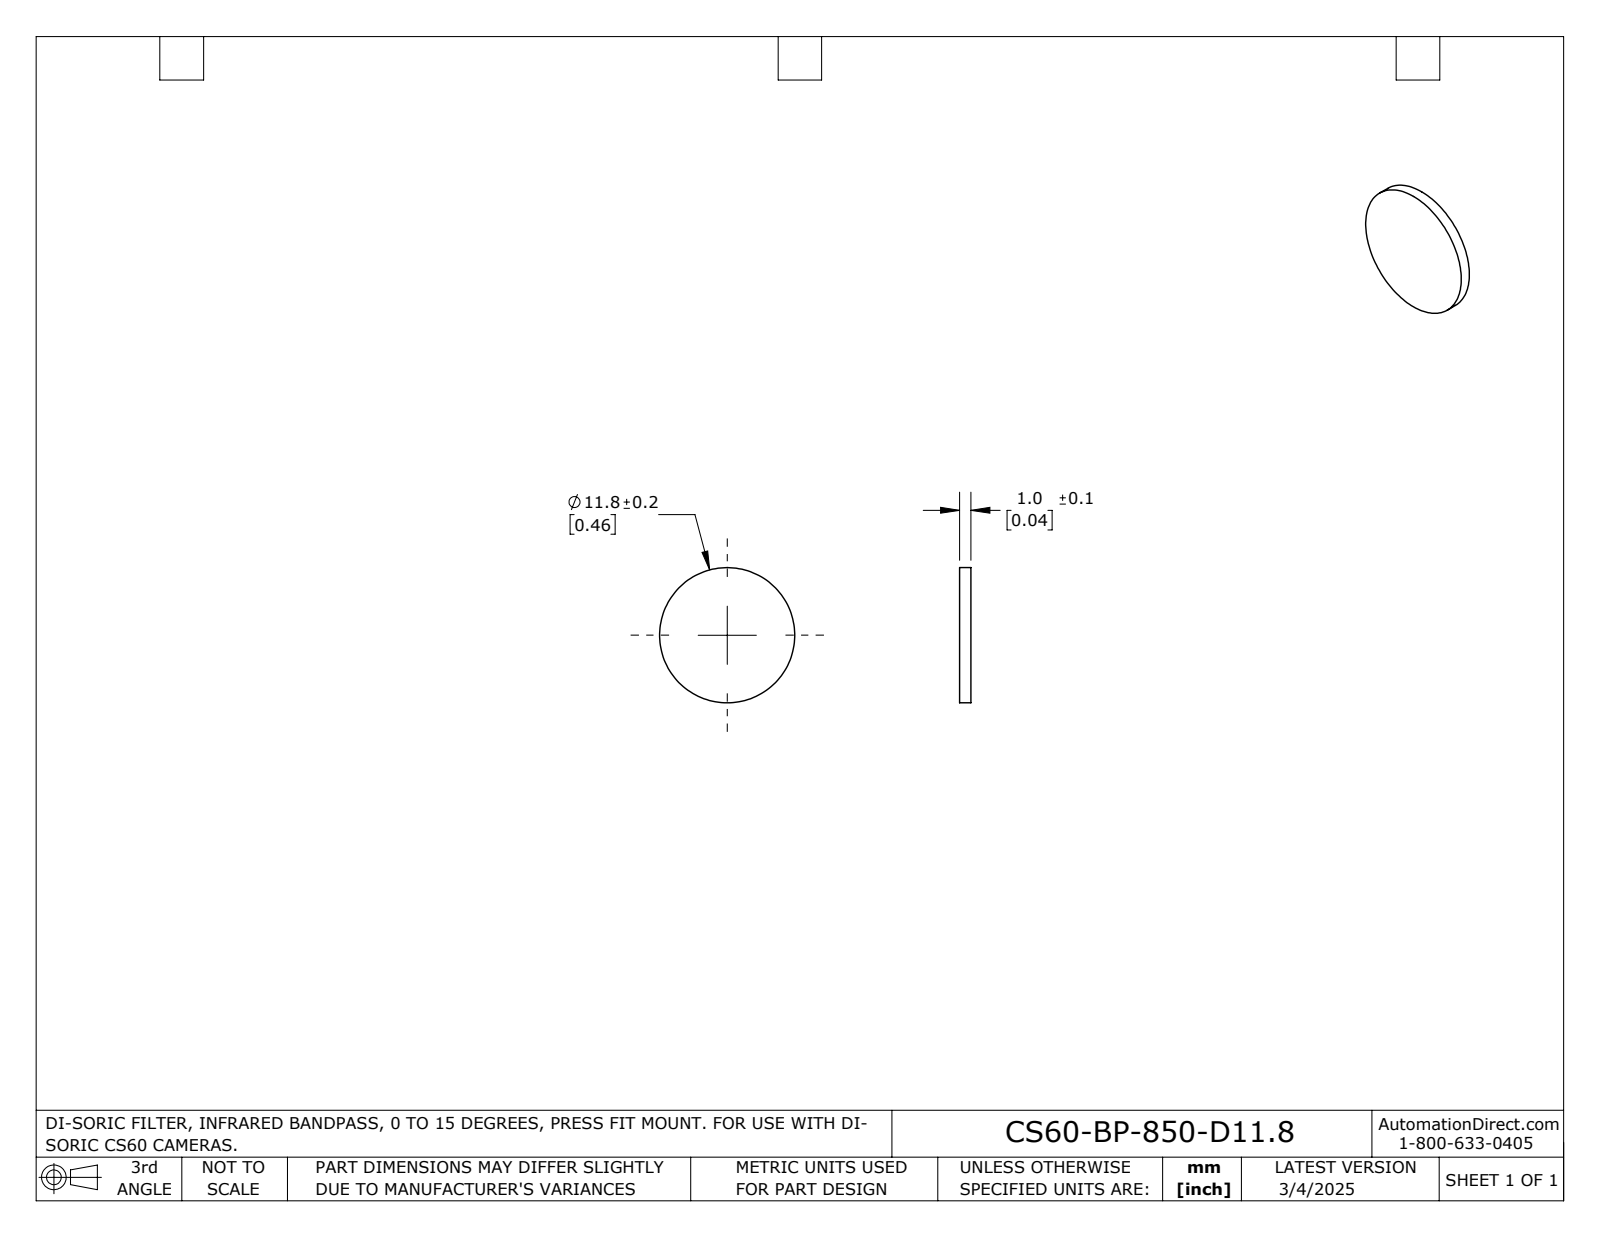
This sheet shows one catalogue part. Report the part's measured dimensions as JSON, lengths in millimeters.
{"part_name": "CS60-BP-xxx-D11.8", "step_written_by": "SolidWorks 2024 (AUTOMOTIVE_DESIGN)", "units": "millimeters", "bodies": {"solids": 1, "faces": 3, "planar": 2, "cylindrical": 1, "other": 0}, "overall_size": [11.8, 11.8, 1], "volume_mm3": 109, "surface_area_mm2": 256, "round_bosses_or_shafts": [[11.8, 1]], "face_to_face_distances": [1]}
